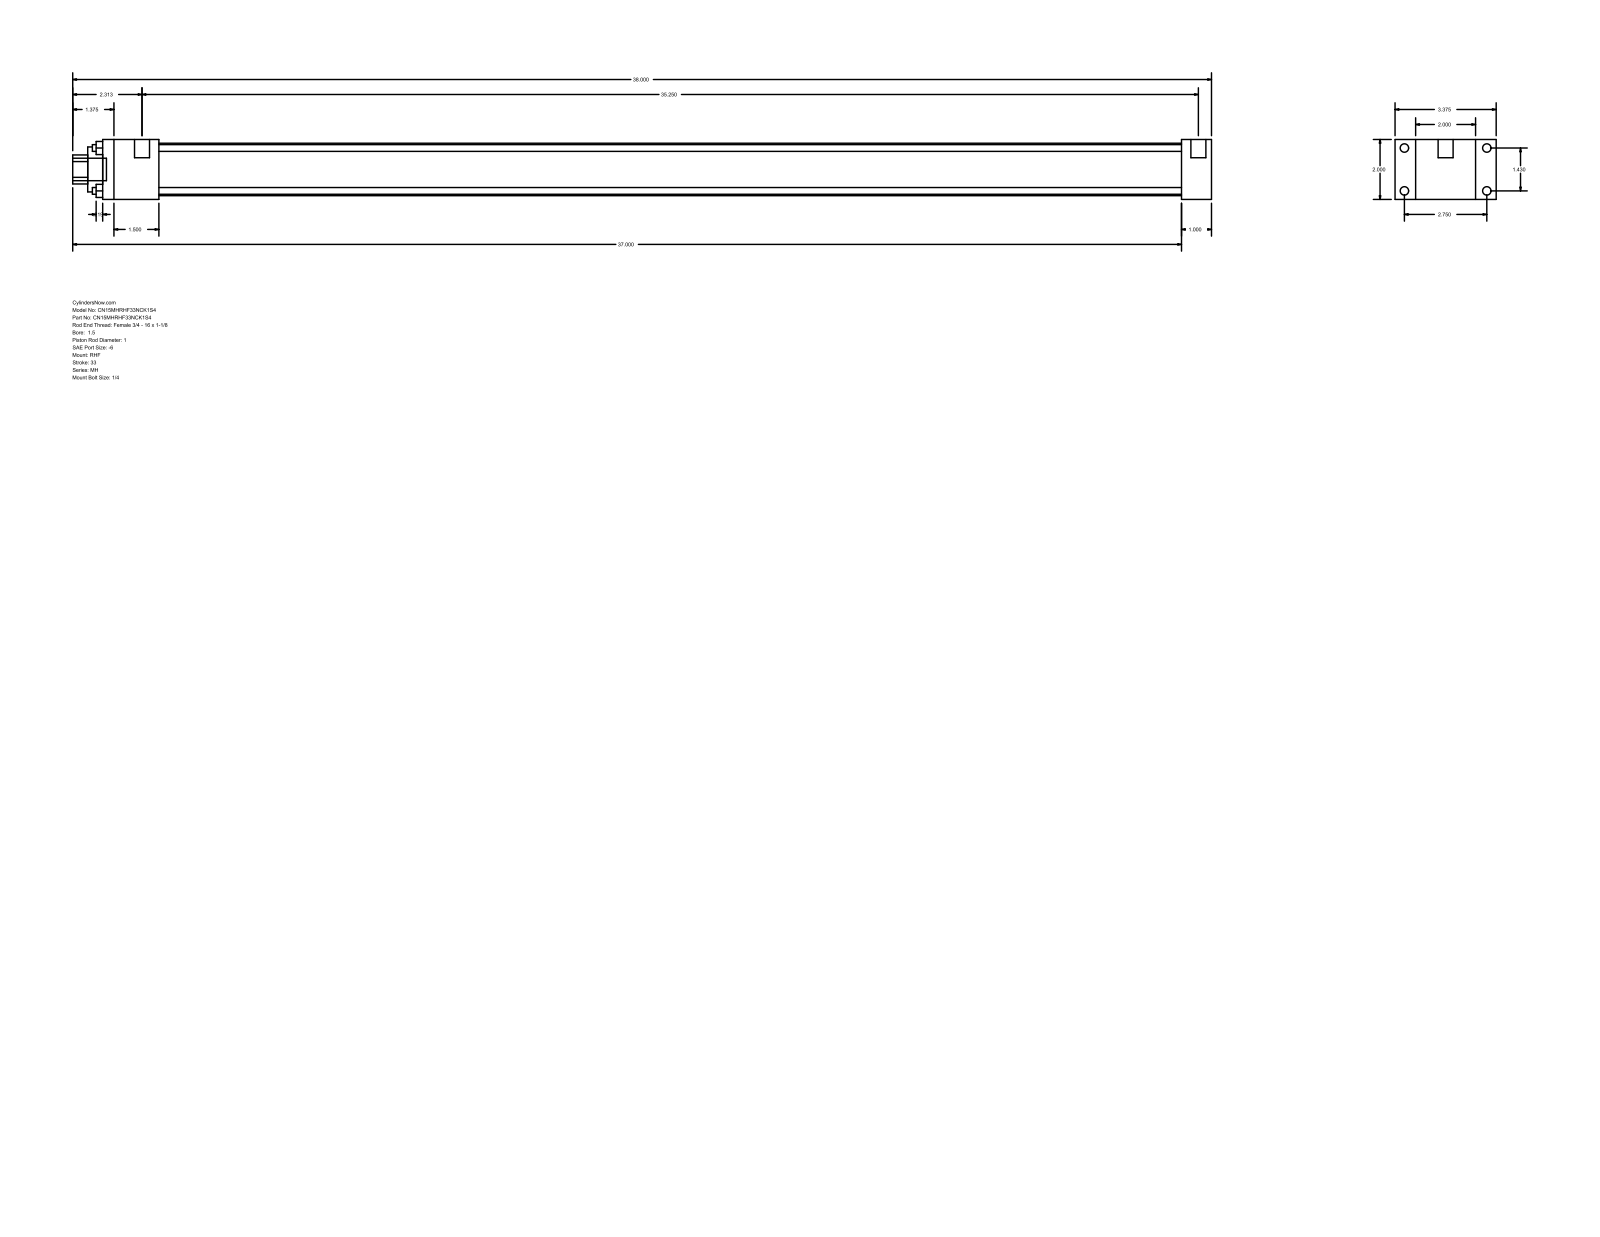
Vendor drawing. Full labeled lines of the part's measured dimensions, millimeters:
Part name (STEP PRODUCT): MH_RHF__0150_1
STEP written by: GSSL Pune (CONFIG_CONTROL_DESIGN)
Units: millimetres
Bodies: 0 solids, 88 faces (60 planar, 28 cylindrical, 0 other)
Overall size (bounding box): 965.2 × 85.72 × 50.8
Round holes (diameter × count): ⌀5.71 ×4, ⌀25.4 ×1, ⌀38.1 ×1, ⌀44.45 ×1
Round bosses / shafts (diameter × count): ⌀7.14 ×4, ⌀5.56 ×4, ⌀12.7 ×2, ⌀19.05 ×1
Partial cylindrical surfaces — rounded edges, fillets, slot ends (radius × count): R12.29 ×1
Main face-to-face distances: 50.8, 25.4, 17.46, 68.26, 85.72, 939.8, 914.4, 47.63, 866.77, 892.17
Hole centre spacings: 25.68, 36.32, 51.36
